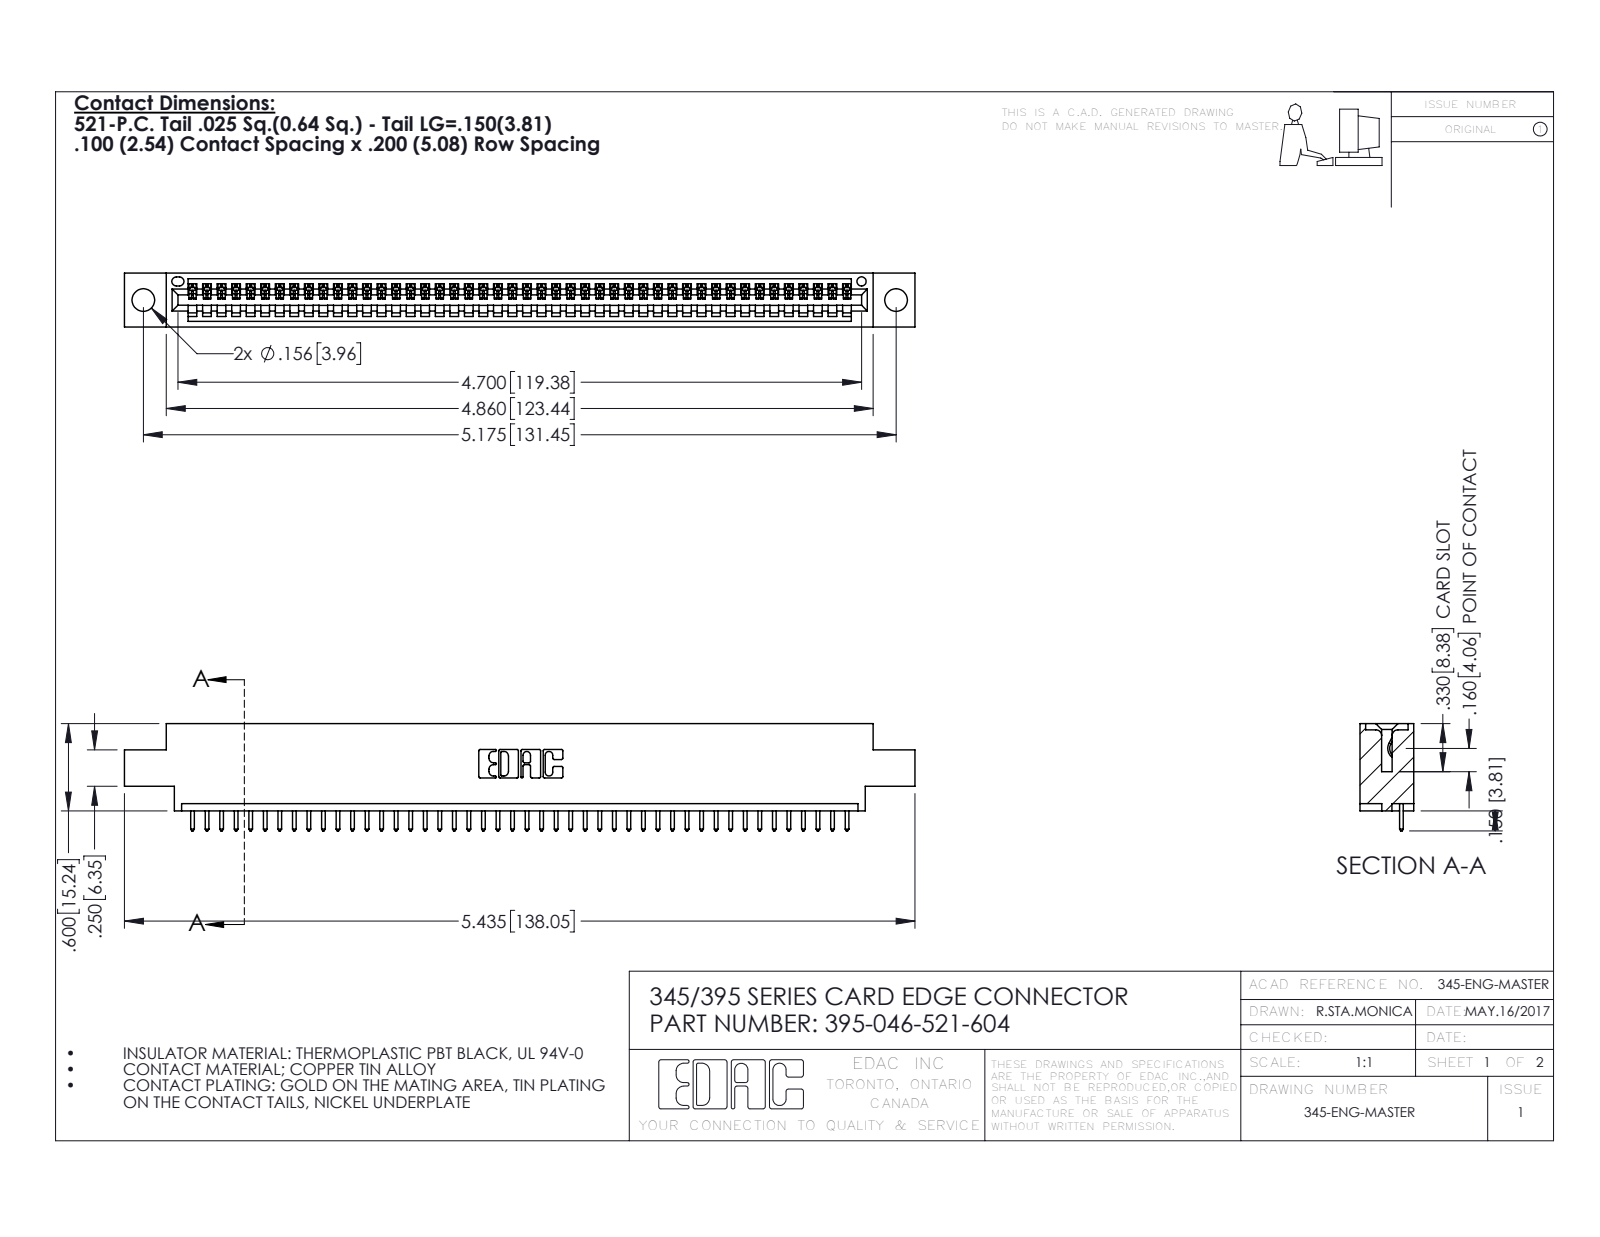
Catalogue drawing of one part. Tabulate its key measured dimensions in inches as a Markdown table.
| quantity | value |
| --- | --- |
| part name | 395-046-521-604; 345-292-001_345-293-121; 345 Part_0.170 Offset - 0.156 Dia-TH |
| STEP written by | SolidWorks 2016 (CONFIG_CONTROL_DESIGN) |
| units | inches |
| bodies | 47 solids, 2798 faces (1924 planar, 874 cylindrical, 0 other) |
| overall size | 5.435 × 0.737 × 0.37 |
| volume | 0.782 in³ |
| surface area | 25.58 in² |
| round holes (diameter × count) | 0.156 × 2, 0.064 × 1 |
| partial cylindrical surfaces (radius × count) | 0.006 × 92, 0.01 × 92, 0.01 × 22, 0.007 × 6, 0.031 × 6, 0.026 × 3, 0.031 × 2, 0.04 × 2 |
| main face-to-face distances | 0.298, 0.072, 0.37, 0.2, 0.098, 0.272, 0.025, 0.225, 0.175, 0.149 |
| hole center spacings | 0.27, 4.939, 5.175 |
